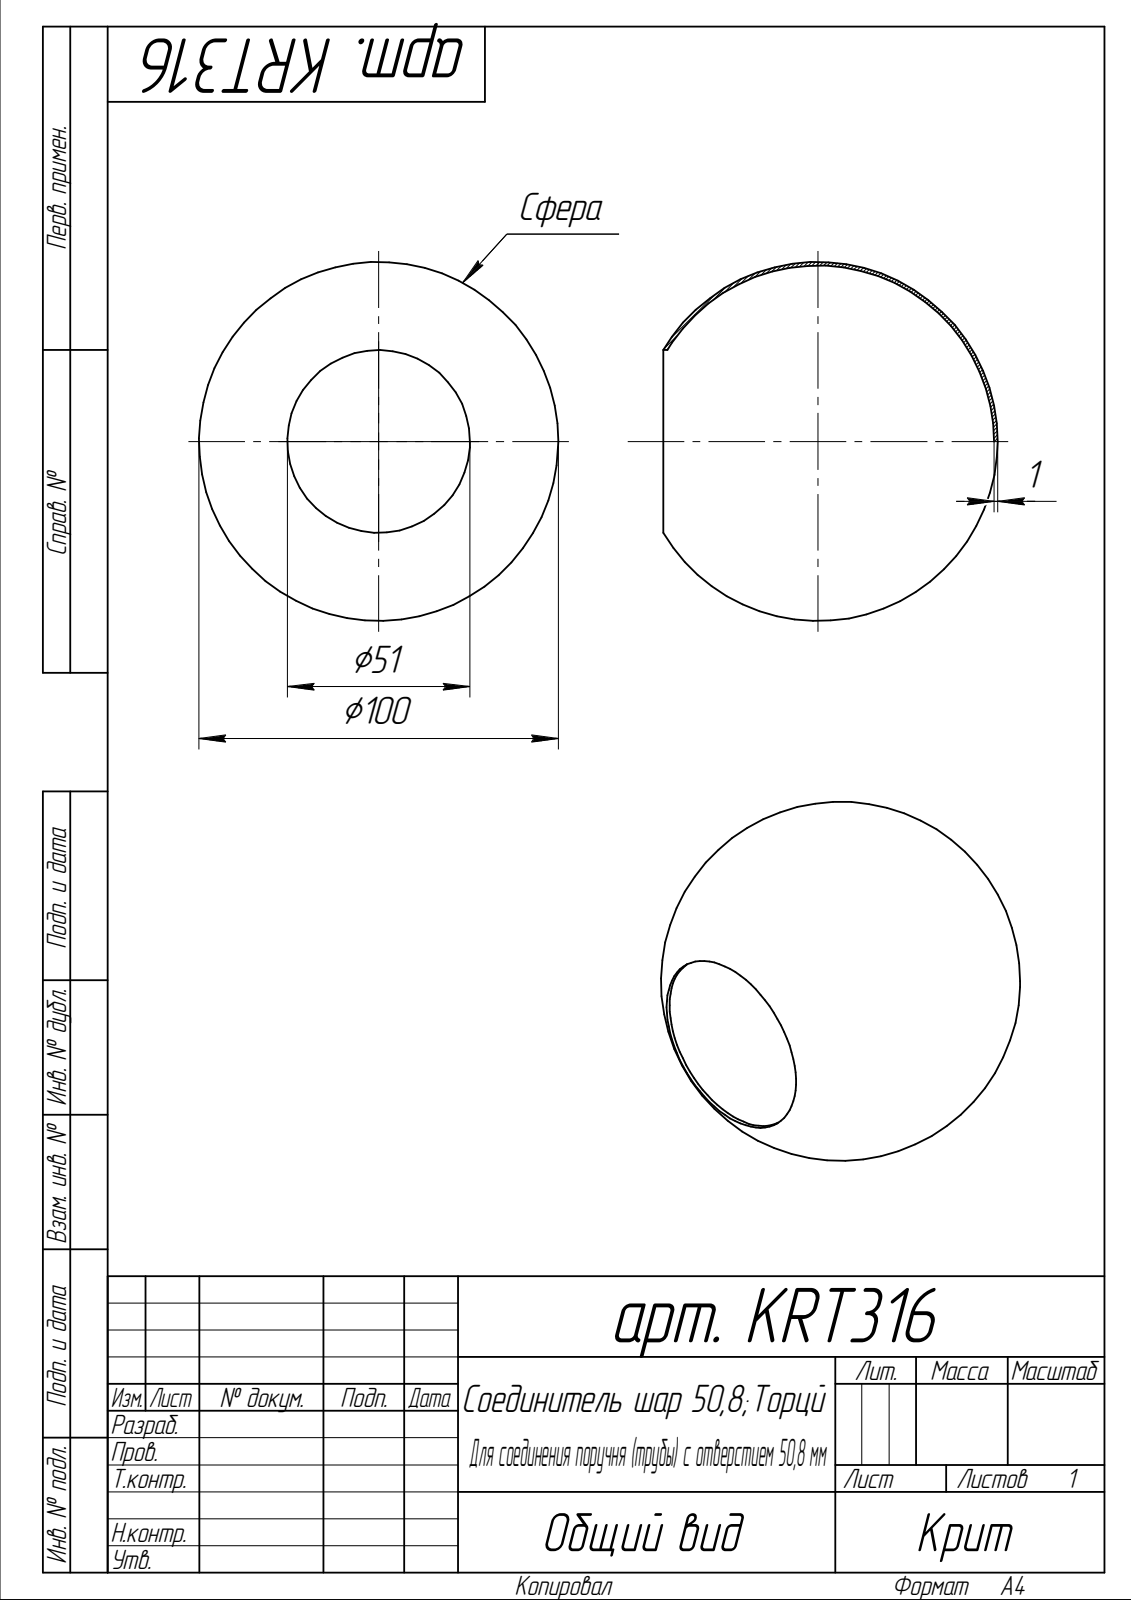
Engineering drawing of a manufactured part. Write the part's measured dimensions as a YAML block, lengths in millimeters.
part_name: "арт. KRT316"
step_written_by: "SolidWorks 2014 (AUTOMOTIVE_DESIGN)"
units: millimeters
bodies: {solids: 1, faces: 6, planar: 0, cylindrical: 2, other: 4}
overall_size: [100, 100, 93.04]
volume: 28601
surface_area: 57393
round_holes:
  - {diameter: 50.9, count: 1}
